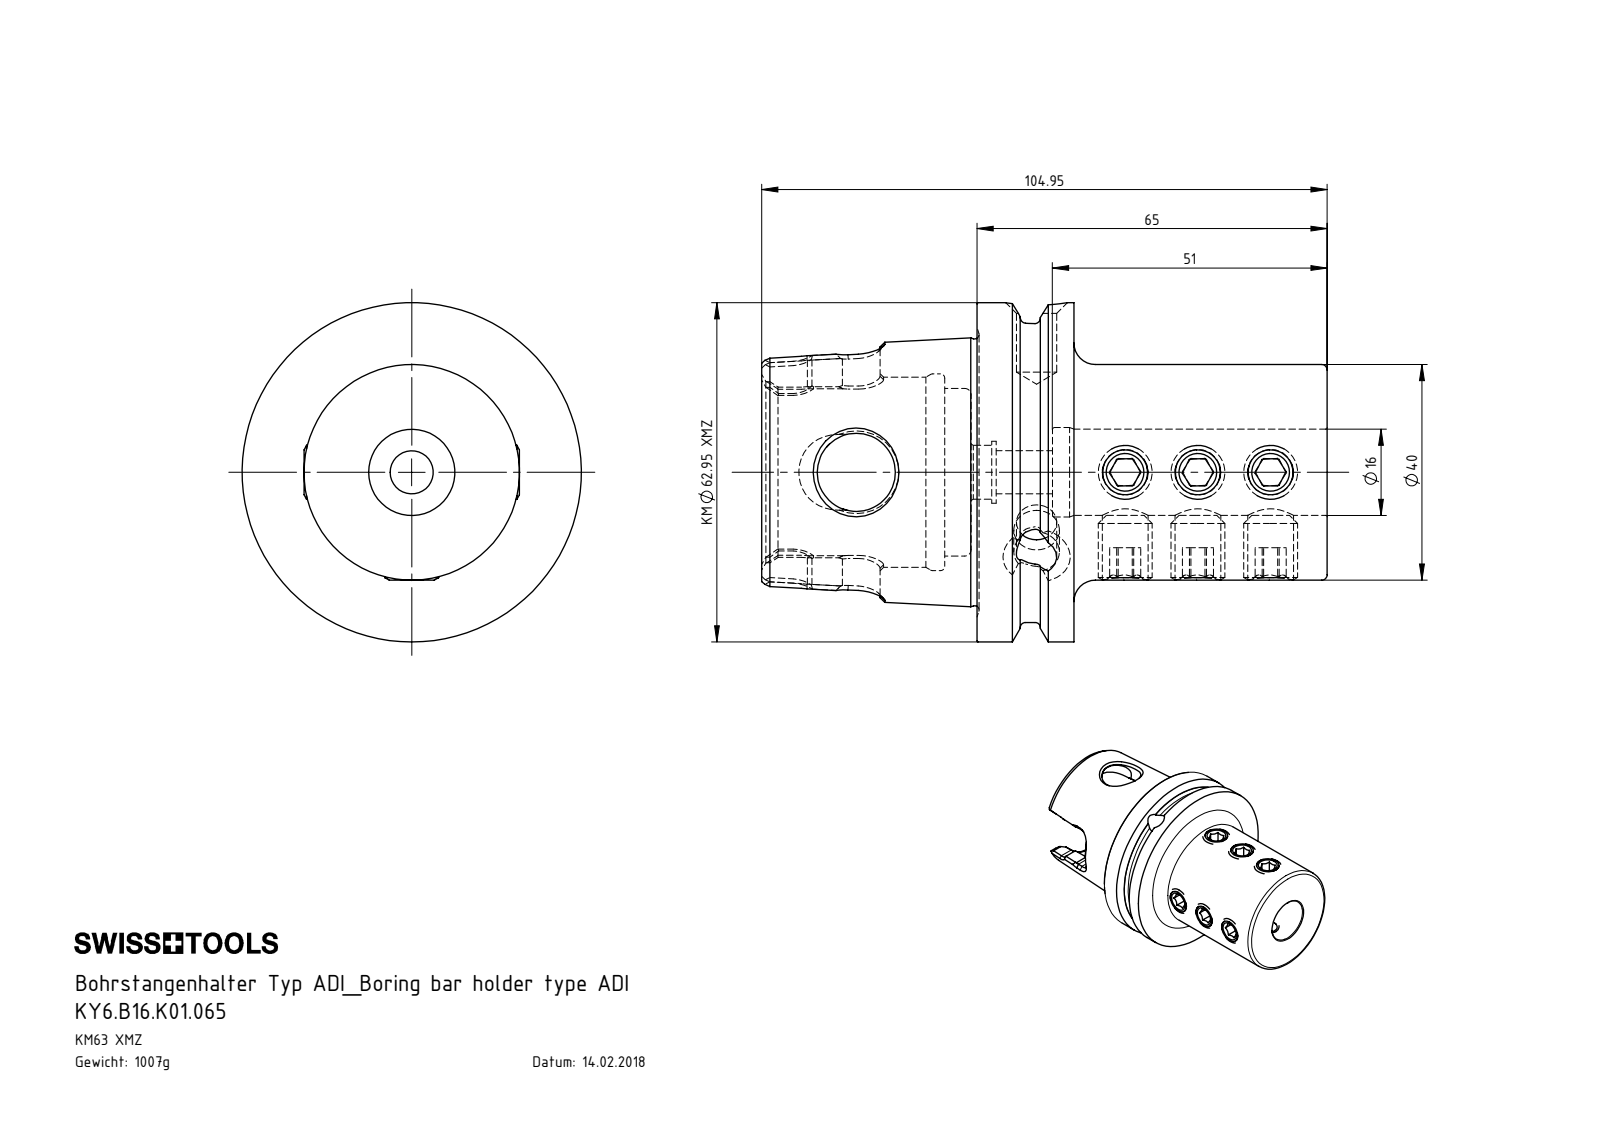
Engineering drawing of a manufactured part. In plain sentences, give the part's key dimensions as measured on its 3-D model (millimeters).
The part is named "KY6.B16.K01.065; KY6-B16.K01.065_A; ISO 4026 - M10 x 12_PreviewCfg". Its 3-D file was written by "SolidWorks 2017 (CONFIG_CONTROL_DESIGN)". It is 10 solids with 388 faces: 127 planar, 88 cylindrical and 173 other. Overall it measures 104.95 by 62.95 by 62.95 millimeters. Its volume is 128 258 cubic millimeters and its surface area 35 495 square millimeters. Round holes: 6 of diameter 8.5, 2 of diameter 7.47, 1 of diameter 8, 1 of diameter 8.48, 1 of diameter 10, 1 of diameter 11.5, 1 of diameter 14.5, 1 of diameter 16, 1 of diameter 16.6, 1 of diameter 31.1, 1 of diameter 35.27, 1 of diameter 36.5. Round bosses or shafts: 6 of diameter 10, 1 of diameter 62.95, 1 of diameter 55.7, 1 of diameter 40. Partial cylindrical surfaces (rounded edges, fillets, slot ends): 6 of radius 4, 2 of radius 7.04. The main face-to-face distances are 47, 18, 65, 1.1, 19.1, 66.1, 6, 5, 12, 4.9. The hole center spacings are 13.5, 27, 16.45, 29.95, 43.45, 49.9, 63.4, 76.9.
